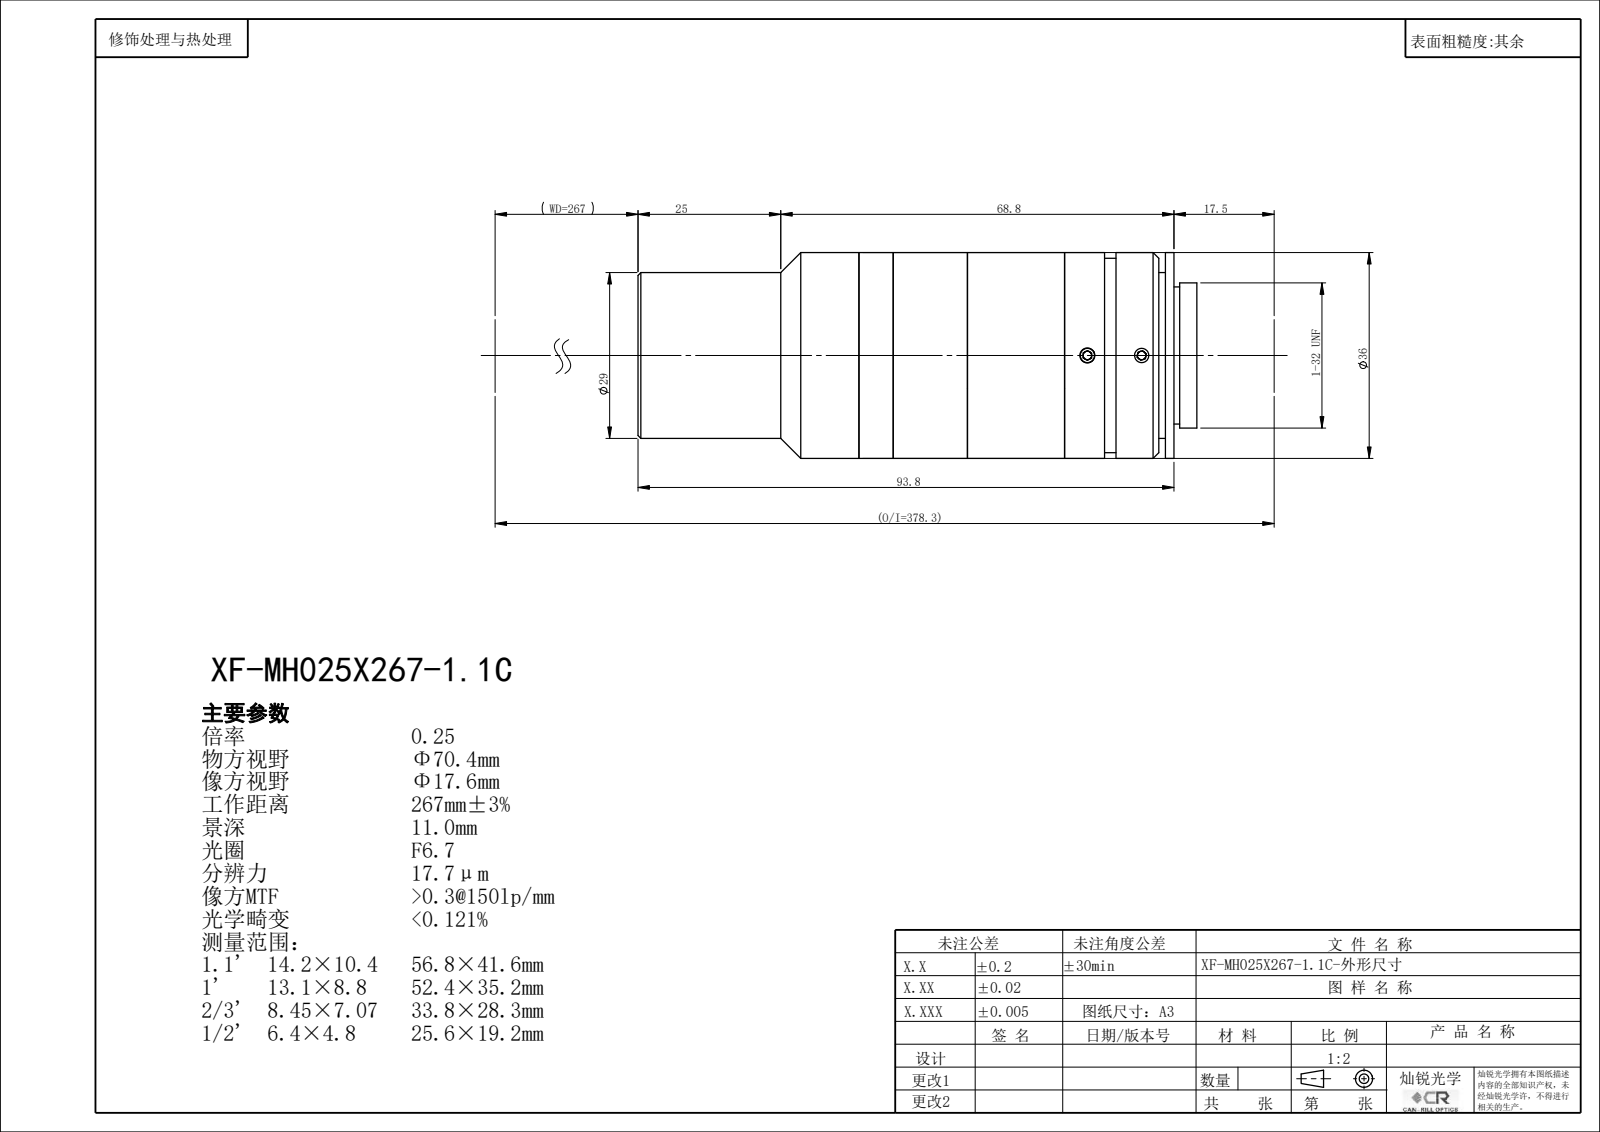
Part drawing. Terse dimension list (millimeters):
name: XF-MH025X267-1.1C
written by: SolidWorks 2022 (CONFIG_CONTROL_DESIGN)
unit: mm
bodies: 0 solids, 141 faces (71 planar, 42 cylindrical, 28 other)
size: 97.83 × 36 × 36
holes: 3× ⌀2.5, 1× ⌀20, 1× ⌀22.4, 1× ⌀24, 1× ⌀24.9, 1× ⌀26, 1× ⌀26.4
bosses: 1× ⌀36, 1× ⌀34, 1× ⌀29, 1× ⌀25.4
face distances: 19.15, 1.5, 17.65, 17, 34.65, 36.15, 6, 23, 11.65, 13.15
